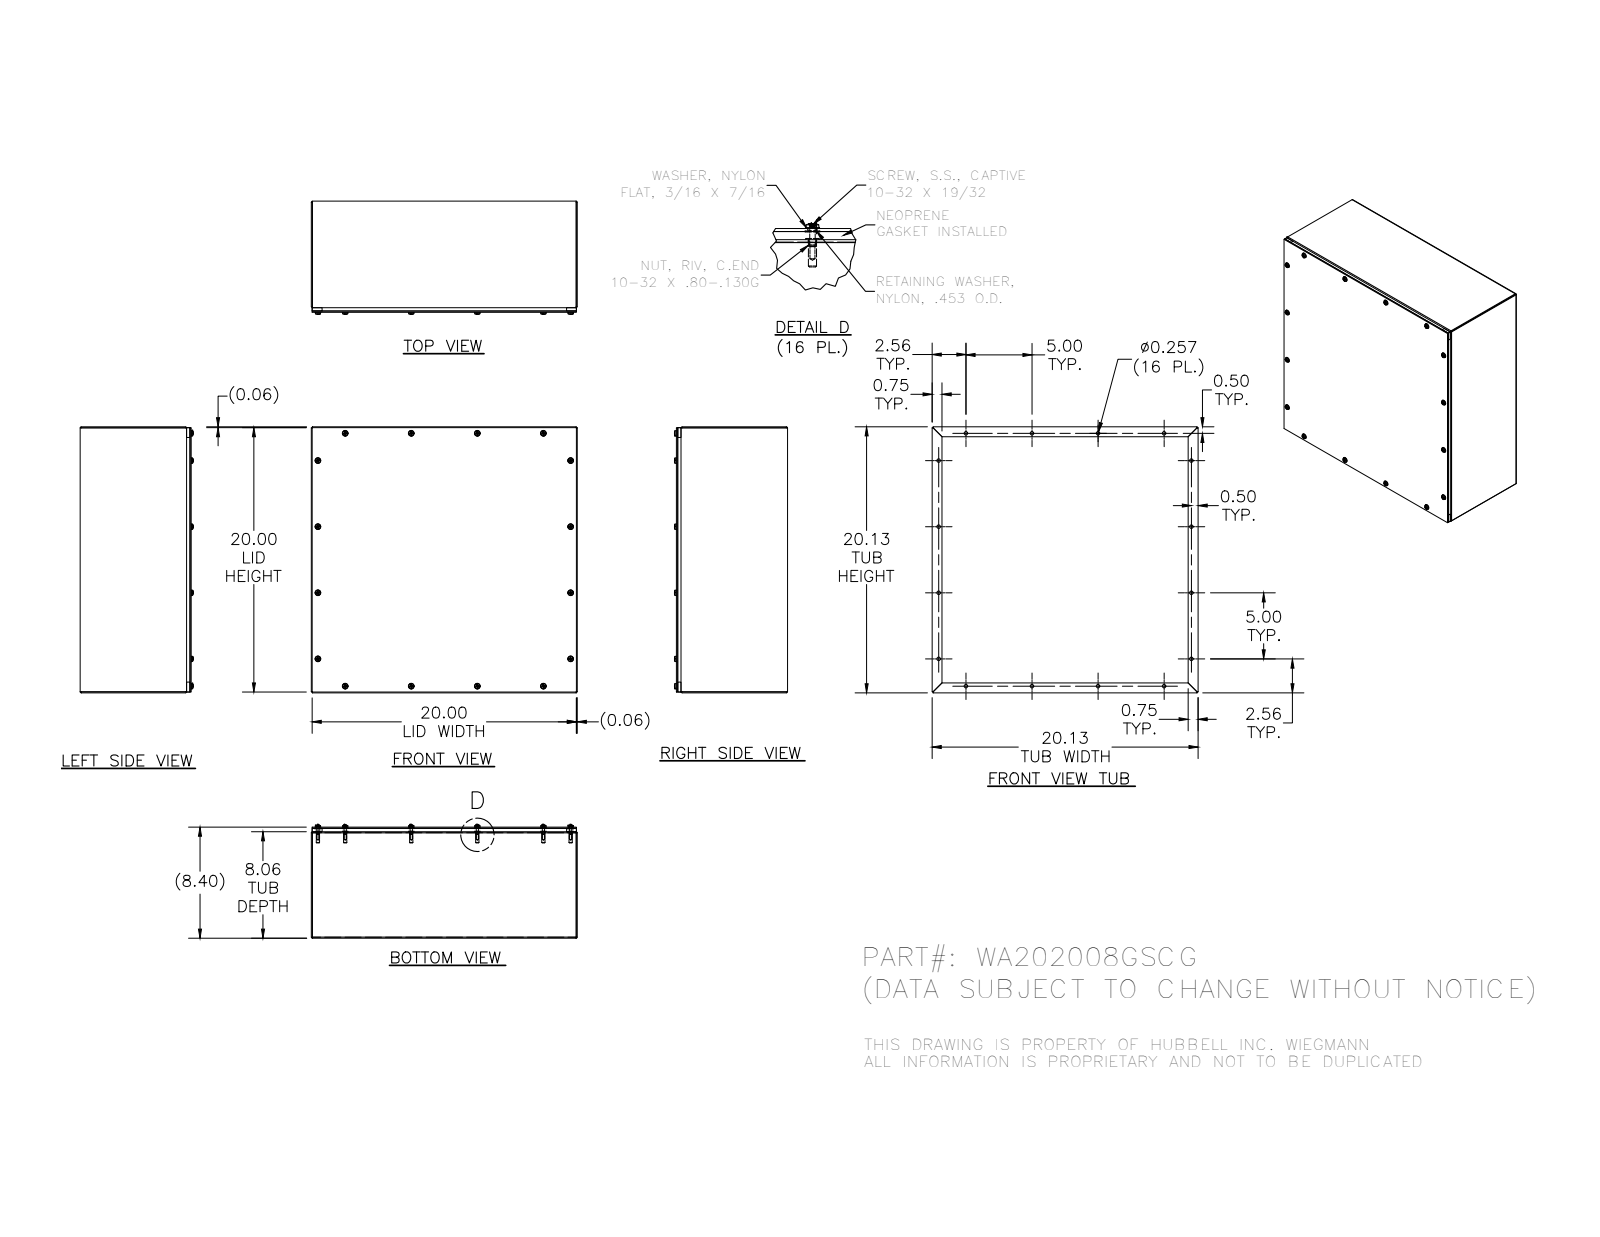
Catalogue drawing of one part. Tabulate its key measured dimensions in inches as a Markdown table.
| quantity | value |
| --- | --- |
| part name | 39035; WA202008GSCGBKP; 37210; 34984 (+3 more) |
| STEP written by | SolidWorks 2014 (AUTOMOTIVE_DESIGN) |
| units | inches |
| bodies | 70 solids, 1652 faces (772 planar, 432 cylindrical, 448 other) |
| overall size | 20.125 × 20.125 × 8.558 |
| volume | 134.1 in³ |
| surface area | 3 203 in² |
| round holes (diameter × count) | 0.156 × 16, 0.188 × 16, 0.196 × 16, 0.257 × 16, 0.278 × 16, 0.281 × 16 |
| round bosses / shafts (diameter × count) | 0.453 × 16, 0.437 × 16, 0.406 × 16, 0.248 × 16, 0.167 × 16 |
| partial cylindrical surfaces (radius × count) | 0.089 × 16, 0.016 × 8, 0.09 × 8 |
| main face-to-face distances | 0.074, 0.094, 8.33, 8.404, 8.236, 8.31, 20.051, 20.125, 19.977, 20.051 |
| hole center spacings | 5, 10, 19.767, 19.768, 19.767, 19.125, 13.977, 13.978 |
